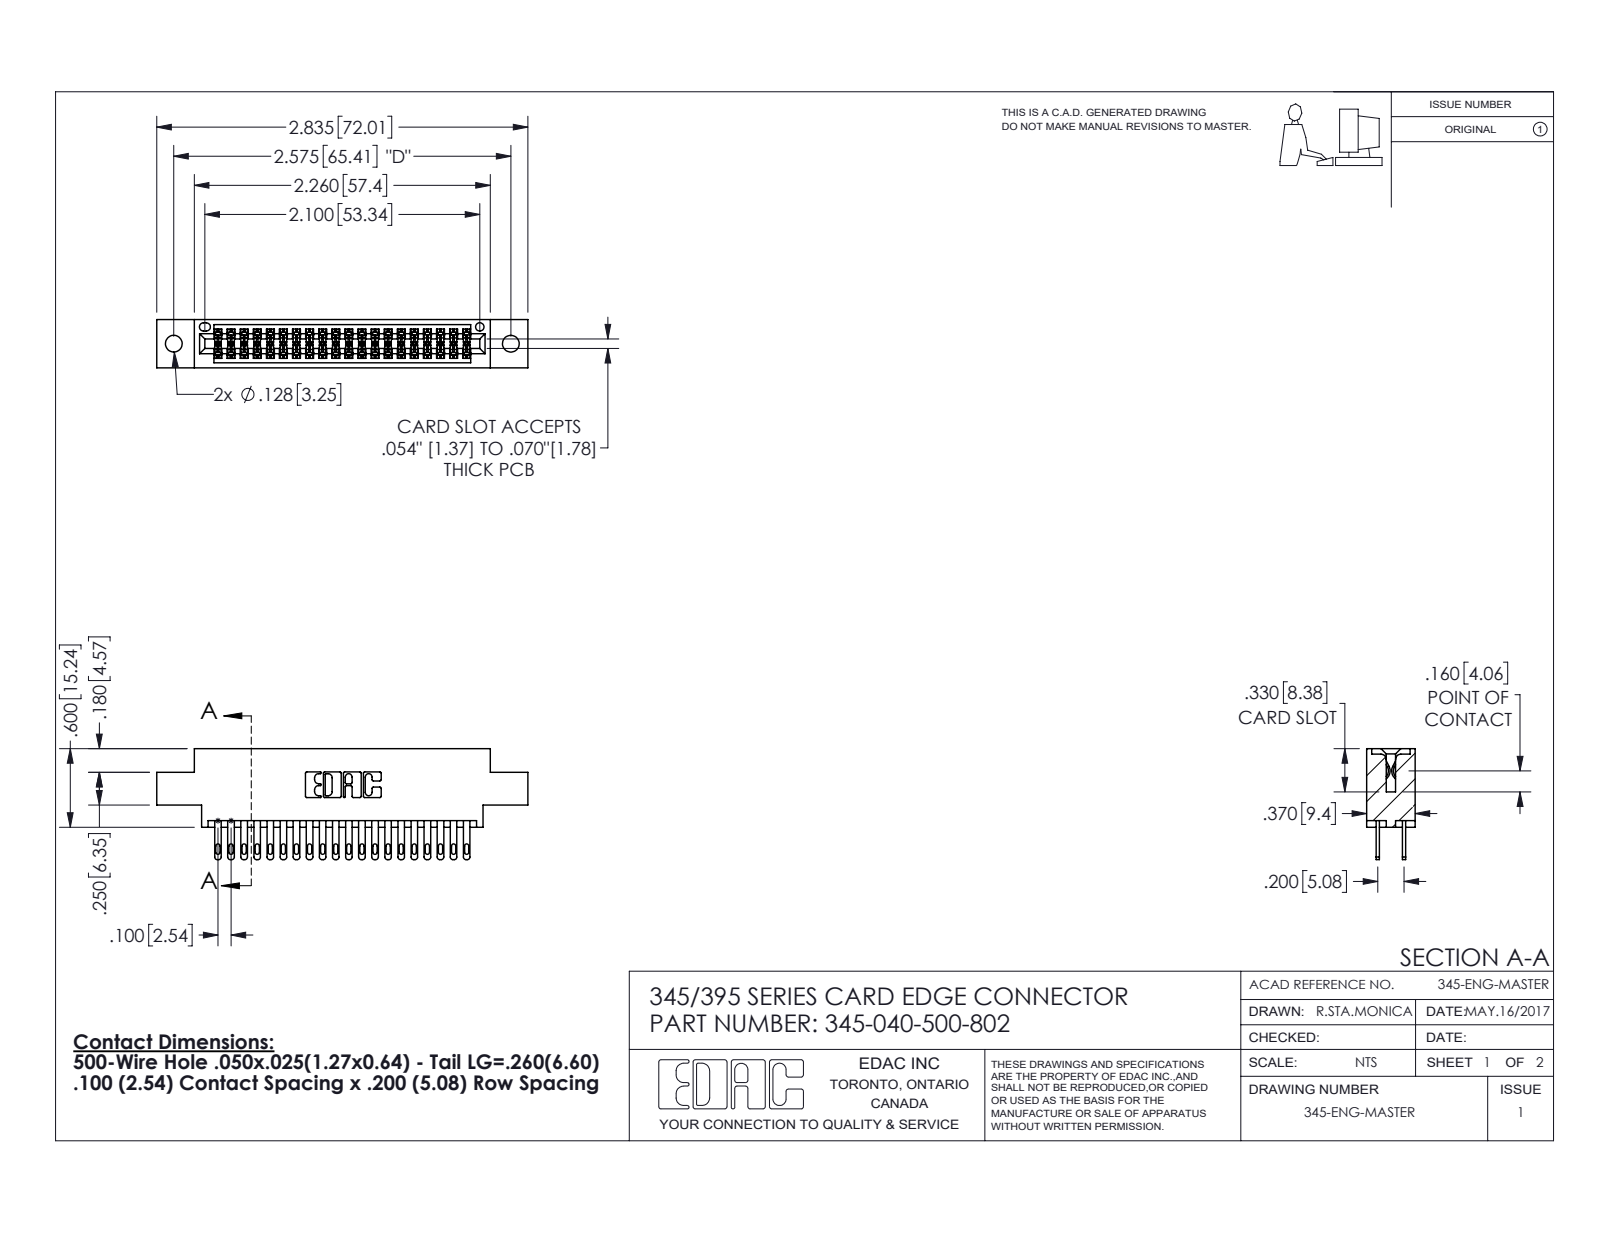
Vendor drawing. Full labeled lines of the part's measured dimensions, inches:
Part name (STEP PRODUCT): 345-040-500-802; 345-292-001_345-293-100; 345 Part_0.170 Offset - 0.128 Dia
STEP written by: SolidWorks 2016 (CONFIG_CONTROL_DESIGN)
Units: inches
Bodies: 41 solids, 1970 faces (1164 planar, 806 cylindrical, 0 other)
Overall size (bounding box): 2.835 × 0.847 × 0.37
Volume: 0.413 in³ · Surface area: 15.27 in²
Round holes (diameter × count): ⌀0.128 ×2, ⌀0.064 ×1
Partial cylindrical surfaces — rounded edges, fillets, slot ends (radius × count): R0.006 ×60, R0.016 ×40, R0.02 ×40, R0.01 ×22, R0.007 ×6, R0.031 ×6, R0.026 ×3, R0.014 ×2
Main face-to-face distances: 0.072, 0.298, 0.2, 0.098, 0.272, 0.025, 0.37, 0.225, 0.175, 0.15
Hole centre spacings: 0.27, 2.341, 2.575
